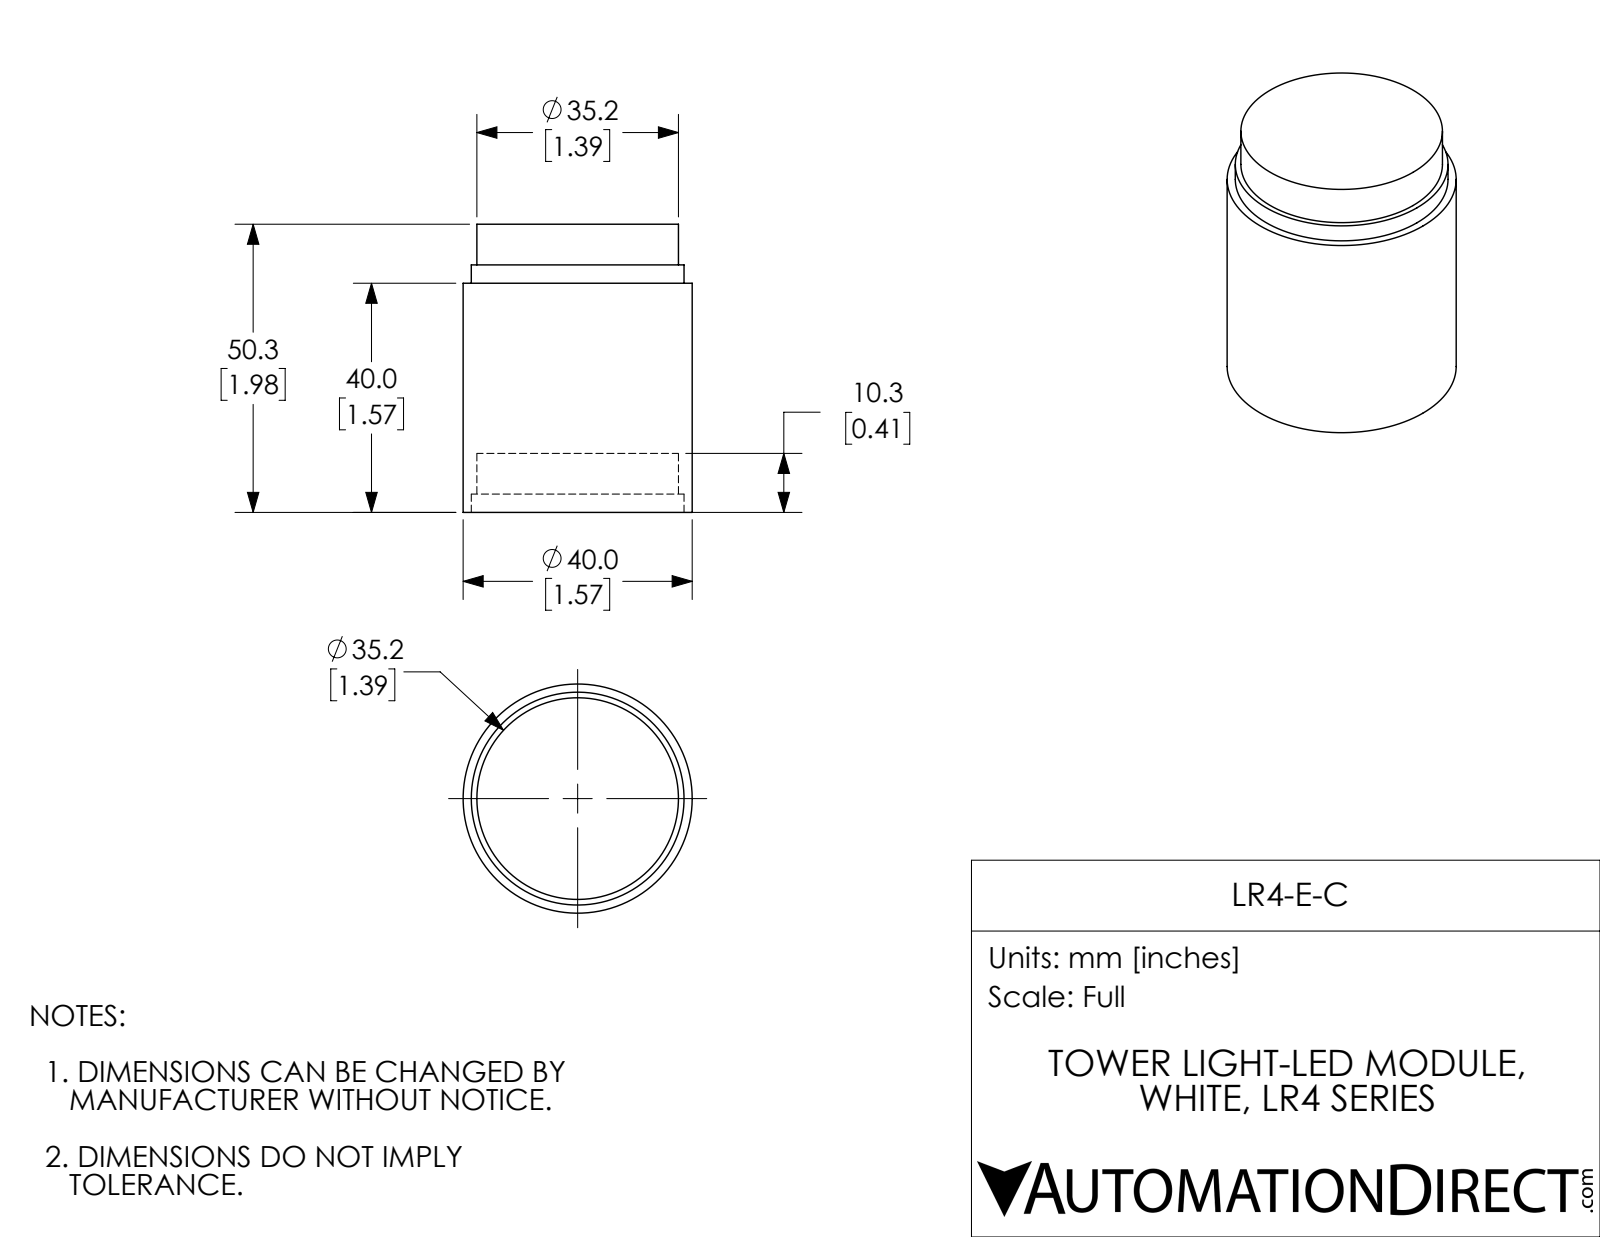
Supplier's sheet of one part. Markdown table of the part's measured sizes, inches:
| quantity | value |
| --- | --- |
| part name | LR4-E-C |
| STEP written by | SolidWorks 2017 (AUTOMOTIVE_DESIGN) |
| units | inches |
| bodies | 1 solid, 16 faces (6 planar, 10 cylindrical, 0 other) |
| overall size | 1.98 × 1.575 × 1.575 |
| volume | 3.067 in³ |
| surface area | 15.28 in² |
| round holes (diameter × count) | 1.386 × 1, 1.463 × 1 |
| round bosses / shafts (diameter × count) | 1.575 × 1 |
| main face-to-face distances | 1.575, 0.406, 0.126, 0.28, 1.98, 1.169, 1.701, 1.295, 1.449, 1.854 |
